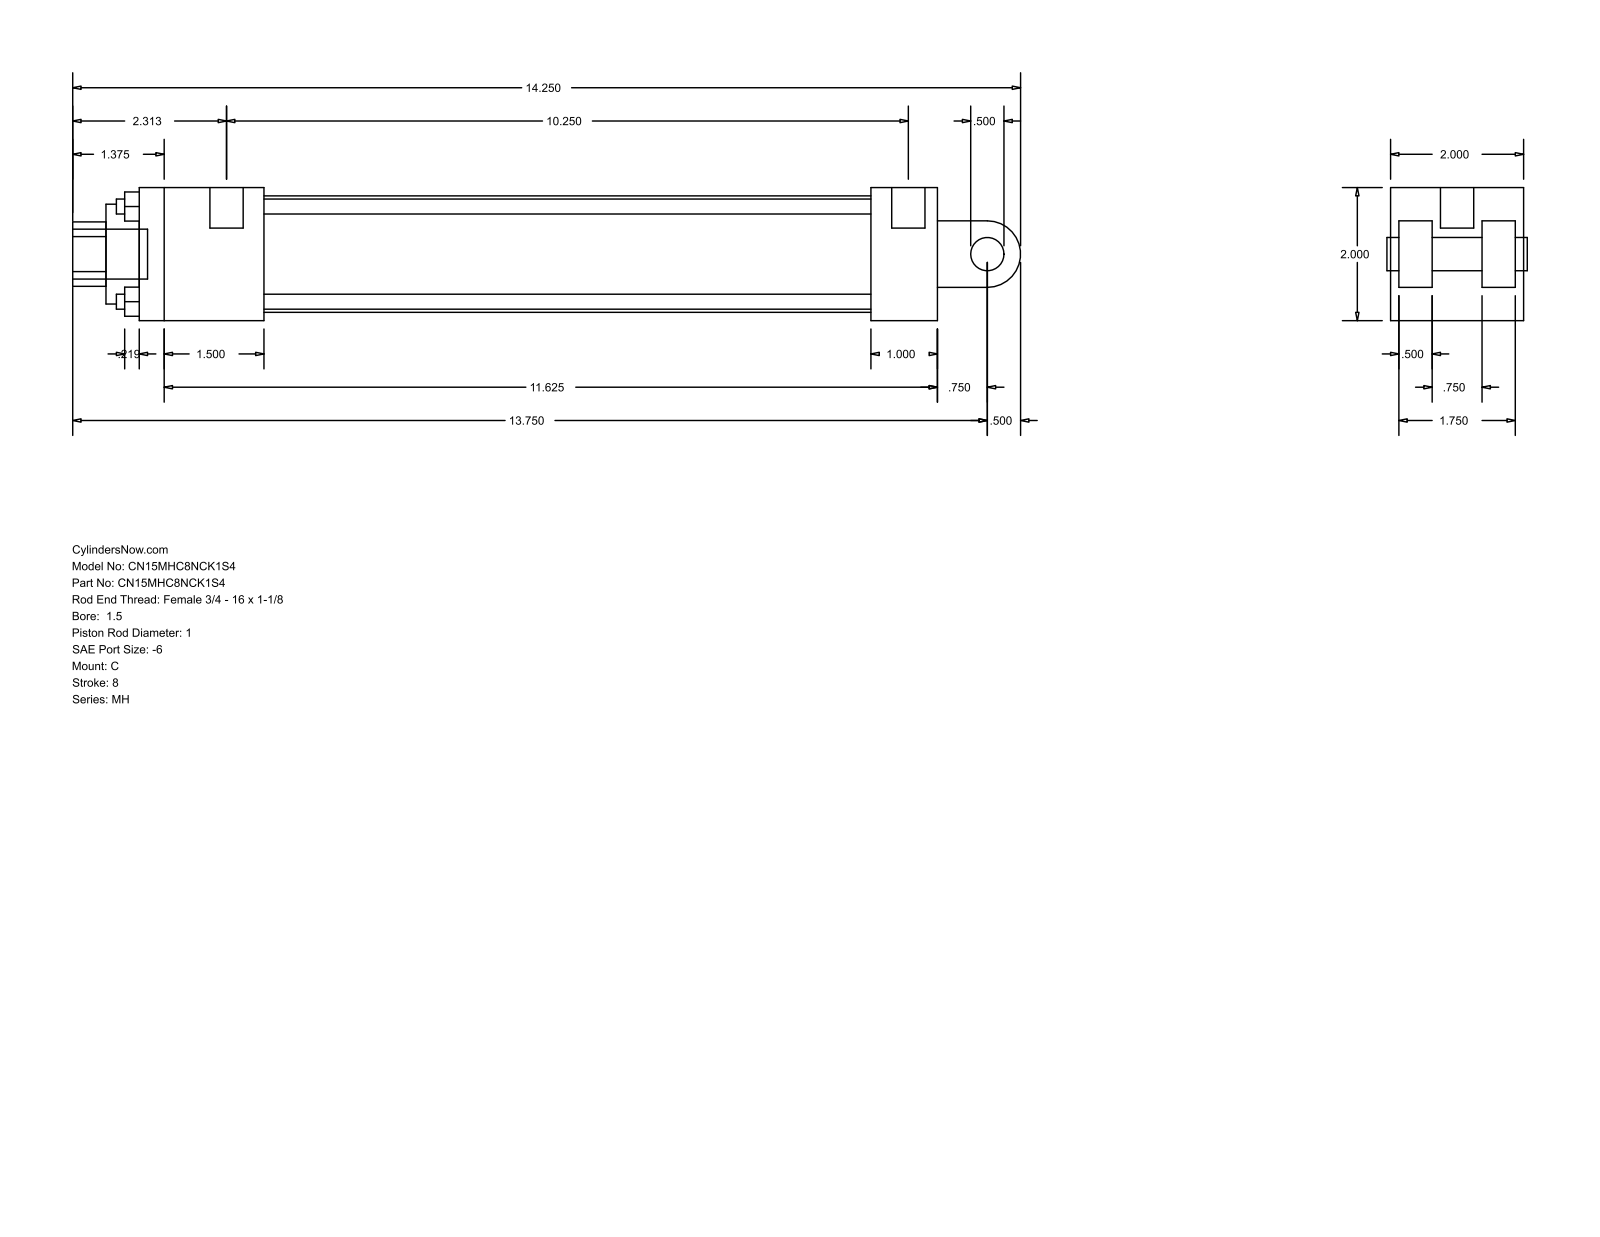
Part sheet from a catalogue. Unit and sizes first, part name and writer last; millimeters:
Units: millimetres
Overall size (bounding box): 361.95 × 50.8 × 50.8
Round holes (diameter × count): ⌀5.71 ×4, ⌀5.56 ×2, ⌀12.7 ×1, ⌀25.4 ×1, ⌀38.1 ×1, ⌀44.45 ×1
Round bosses / shafts (diameter × count): ⌀12.7 ×2, ⌀5.56 ×2, ⌀19.05 ×1
Partial cylindrical surfaces — rounded edges, fillets, slot ends (radius × count): R12.29 ×1, R12.7 ×1
Main face-to-face distances: 50.8, 12.7, 47.63, 3.17, 15.87, 25.4, 34.93, 31.76, 304.8, 38.1
Hole centre spacings: 25.68, 36.32, 51.36
Bodies: 0 solids, 99 faces (70 planar, 29 cylindrical, 0 other)
Part name (STEP PRODUCT): MH_C__0150_1
STEP written by: GSSL Pune (CONFIG_CONTROL_DESIGN)
